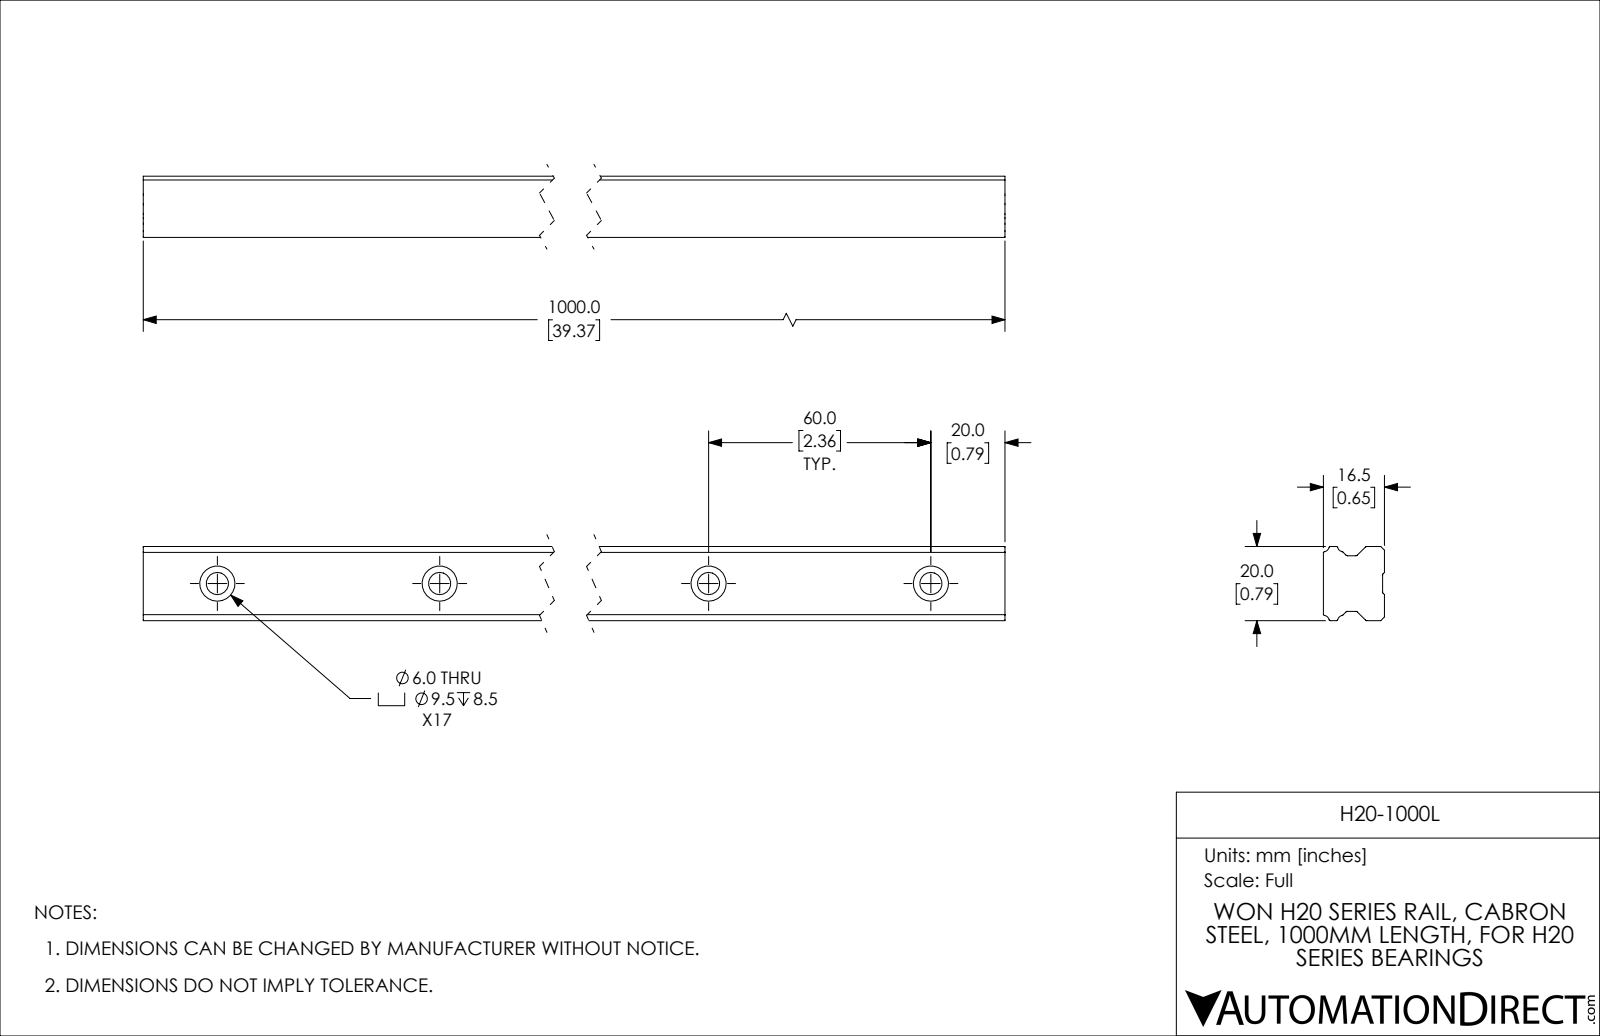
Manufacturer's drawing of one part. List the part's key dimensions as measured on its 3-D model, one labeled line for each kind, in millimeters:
Part name (STEP PRODUCT): H20-1000L
STEP written by: SolidWorks 2019 (CONFIG_CONTROL_DESIGN)
Units: millimetres
Bodies: 1 solid, 210 faces (88 planar, 122 cylindrical, 0 other)
Overall size (bounding box): 1000 × 20 × 16.5
Volume: 281 859 mm³ · Surface area: 81 006 mm²
Round holes (diameter × count): ⌀6 ×17, ⌀9.5 ×17
Partial cylindrical surfaces — rounded edges, fillets, slot ends (radius × count): R0.5 ×12, R0.3 ×4, R1.6 ×4
Main face-to-face distances: 16.5, 20, 2.5, 17.5, 0.5, 16, 8.28, 15, 8.48, 16.96
Hole centre spacings: 60, 120, 180, 240, 300, 360, 420, 480
